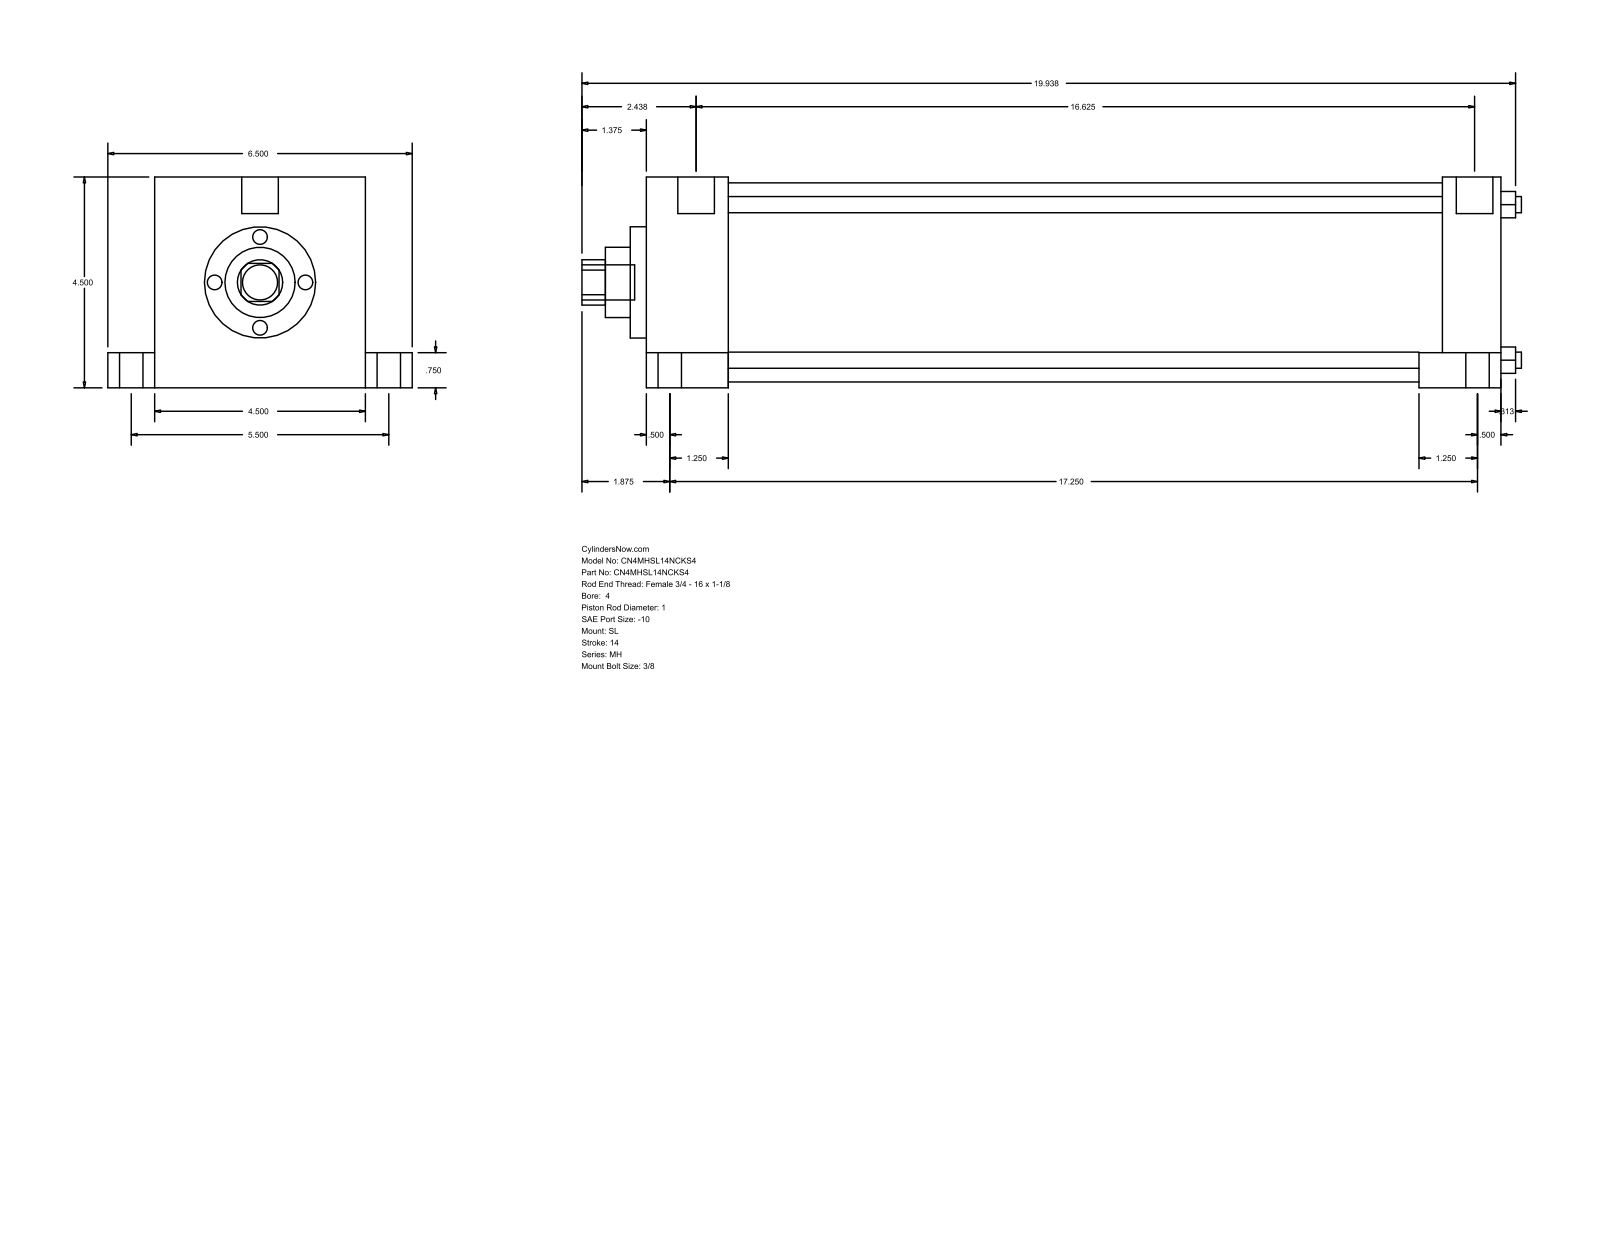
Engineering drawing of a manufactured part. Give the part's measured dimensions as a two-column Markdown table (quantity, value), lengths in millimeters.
| quantity | value |
| --- | --- |
| part name | MH_SL__0400_1 |
| STEP written by | GSSL Pune (CONFIG_CONTROL_DESIGN) |
| units | millimeters |
| bodies | 0 solids, 110 faces (77 planar, 33 cylindrical, 0 other) |
| overall size | 509.59 × 165.1 × 114.3 |
| round holes (diameter × count) | 8.76 × 4, 25.4 × 1, 38.1 × 1, 60.33 × 1, 107.95 × 1 |
| round bosses / shafts (diameter × count) | 19.05 × 5, 12.7 × 4, 8.73 × 4, 19.84 × 2 |
| partial cylindrical surfaces (radius × count) | 12.29 × 1 |
| main face-to-face distances | 114.3, 463.56, 44.46, 419.1, 431.81, 387.35, 31.75, 25.4, 139.7, 19.05 |
| hole center spacings | 59.62, 84.32, 119.25 |
